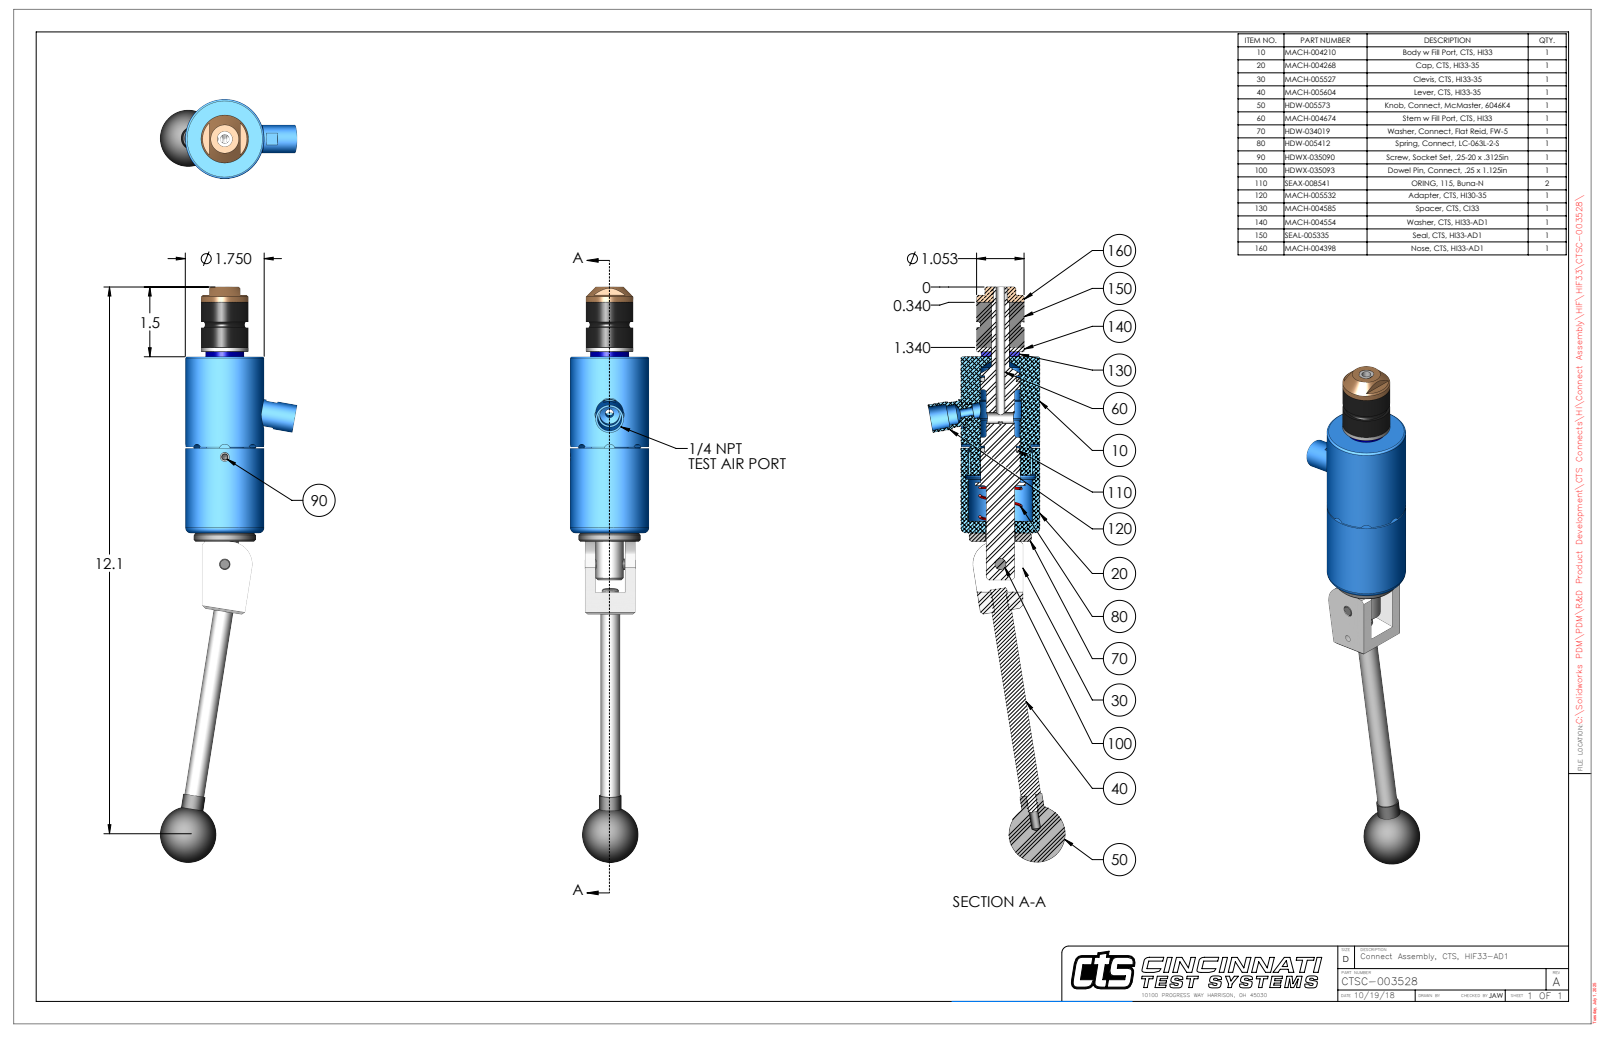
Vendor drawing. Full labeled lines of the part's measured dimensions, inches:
Part name (STEP PRODUCT): CTSC-003528
STEP written by: SolidWorks 2023 (AUTOMOTIVE_DESIGN)
Units: inches
Bodies: 10 solids, 278 faces (91 planar, 122 cylindrical, 65 other)
Overall size (bounding box): 12.751 × 3.043 × 1.75
Volume: 13.77 in³ · Surface area: 76.45 in²
Round holes (diameter × count): ⌀0.201 ×2, ⌀0.313 ×2, ⌀0.15 ×1, ⌀0.187 ×1, ⌀0.204 ×1, ⌀0.249 ×1, ⌀0.25 ×1, ⌀0.251 ×1, ⌀0.39 ×1, ⌀0.397 ×1, ⌀0.403 ×1, ⌀0.438 ×1
Round bosses / shafts (diameter × count): ⌀0.375 ×2, ⌀0.312 ×2, ⌀0.25 ×2, ⌀1.75 ×1, ⌀1.38 ×1, ⌀1.053 ×1, ⌀0.858 ×1, ⌀0.625 ×1
Partial cylindrical surfaces — rounded edges, fillets, slot ends (radius × count): R0.125 ×4, R0.029 ×2, R0.148 ×1, R0.33 ×1, R0.5 ×1, R0.695 ×1, R0.829 ×1
Main face-to-face distances: 3.907, 1.207, 5.114, 1, 0.207, 4.114, 1.12, 5.302, 4.302, 4.095
Hole centre spacings: 0.74, 2.376, 3.116
